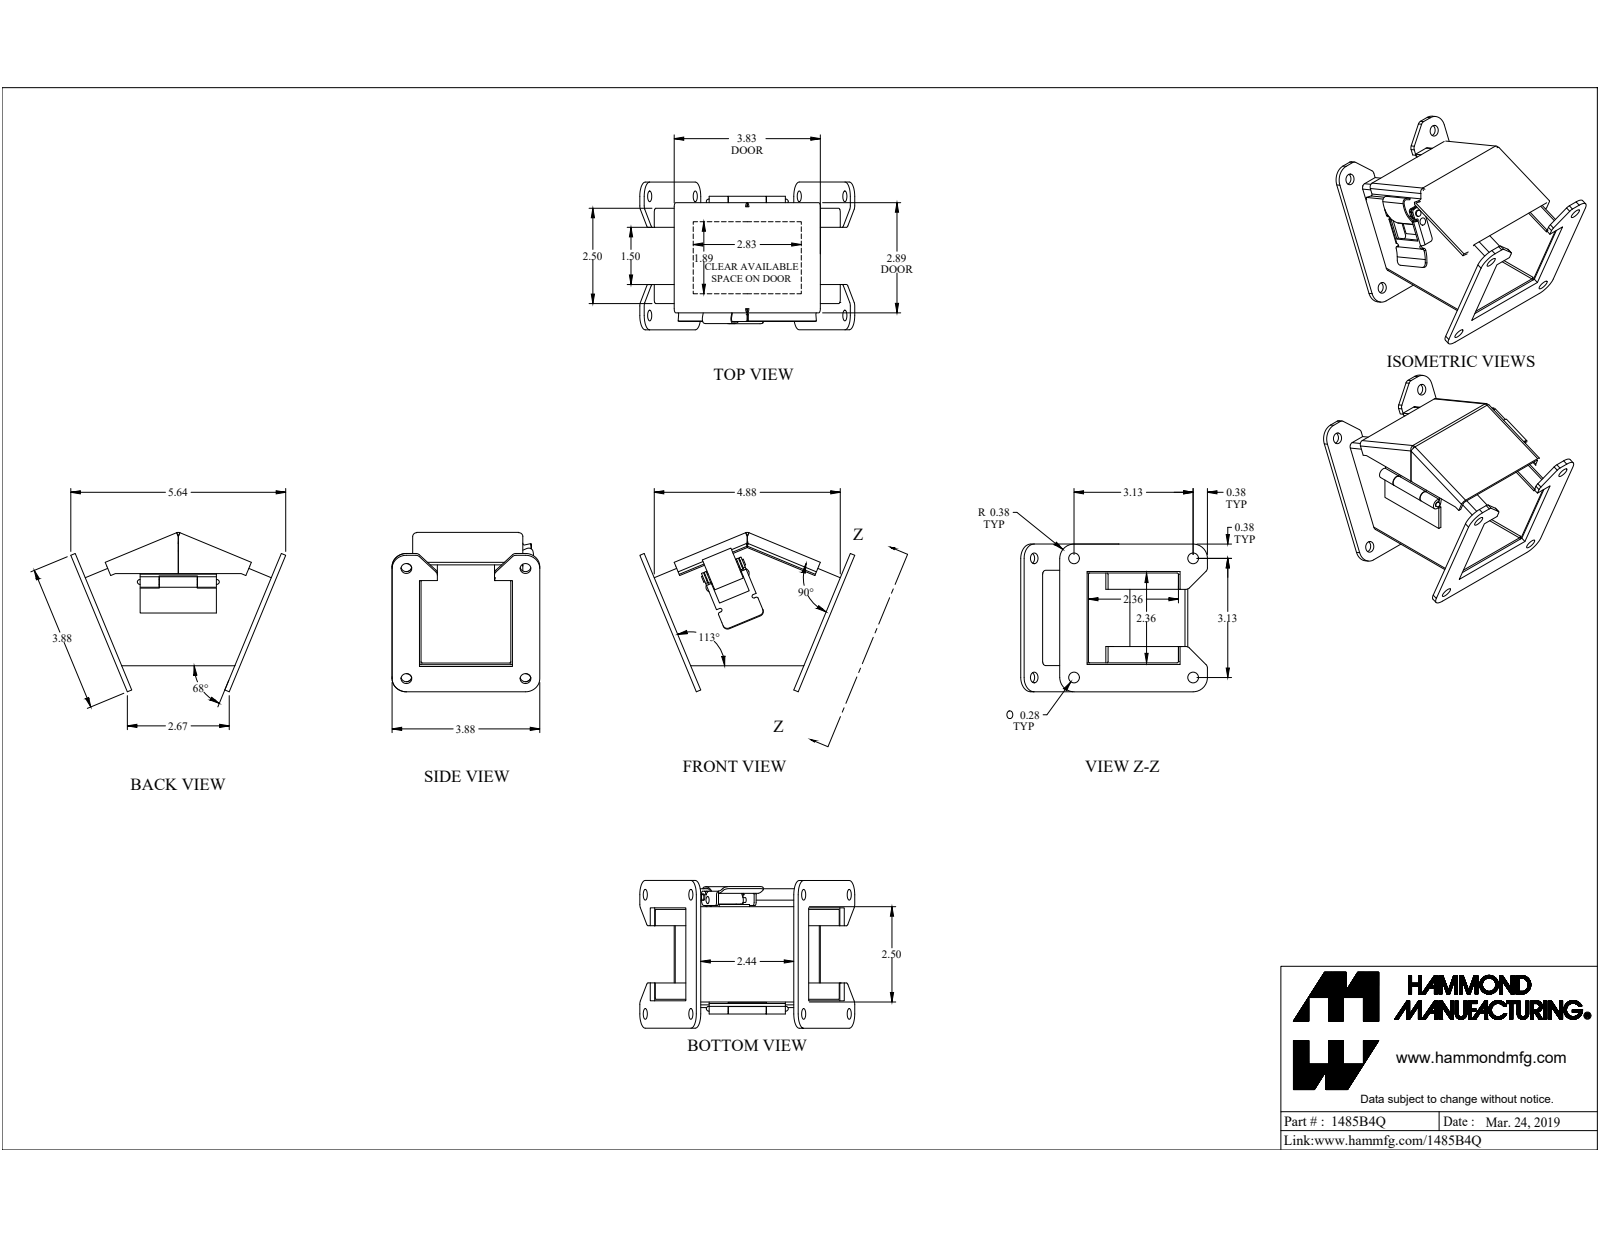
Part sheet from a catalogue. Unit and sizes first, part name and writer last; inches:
Units: inches
Overall size (bounding box): 5.639 × 4.18 × 3.876
Round holes (diameter × count): ⌀0.281 ×8, ⌀0.164 ×2, ⌀0.125 ×1
Round bosses / shafts (diameter × count): ⌀0.162 ×2, ⌀0.158 ×2, ⌀0.275 ×1, ⌀0.125 ×1, ⌀0.125 ×1
Partial cylindrical surfaces — rounded edges, fillets, slot ends (radius × count): R0.036 ×13, R0.108 ×13, R0.125 ×12, R0.375 ×8, R0.029 ×4, R0.078 ×4, R0.086 ×4, R0.015 ×2
Main face-to-face distances: 0.072, 2.428, 0.125, 2.5, 2.356, 0.072, 0.075, 0.174, 2.575, 2.503
Hole centre spacings: 3.125, 4.419, 3.125, 3.175, 0.843, 0.843, 2.285, 2.285
Volume: 5.966 in³ · Surface area: 158.1 in²
Bodies: 10 solids, 282 faces (166 planar, 100 cylindrical, 16 other)
Part name (STEP PRODUCT): 1485B4Q
STEP written by: SolidWorks 2019 (CONFIG_CONTROL_DESIGN)
